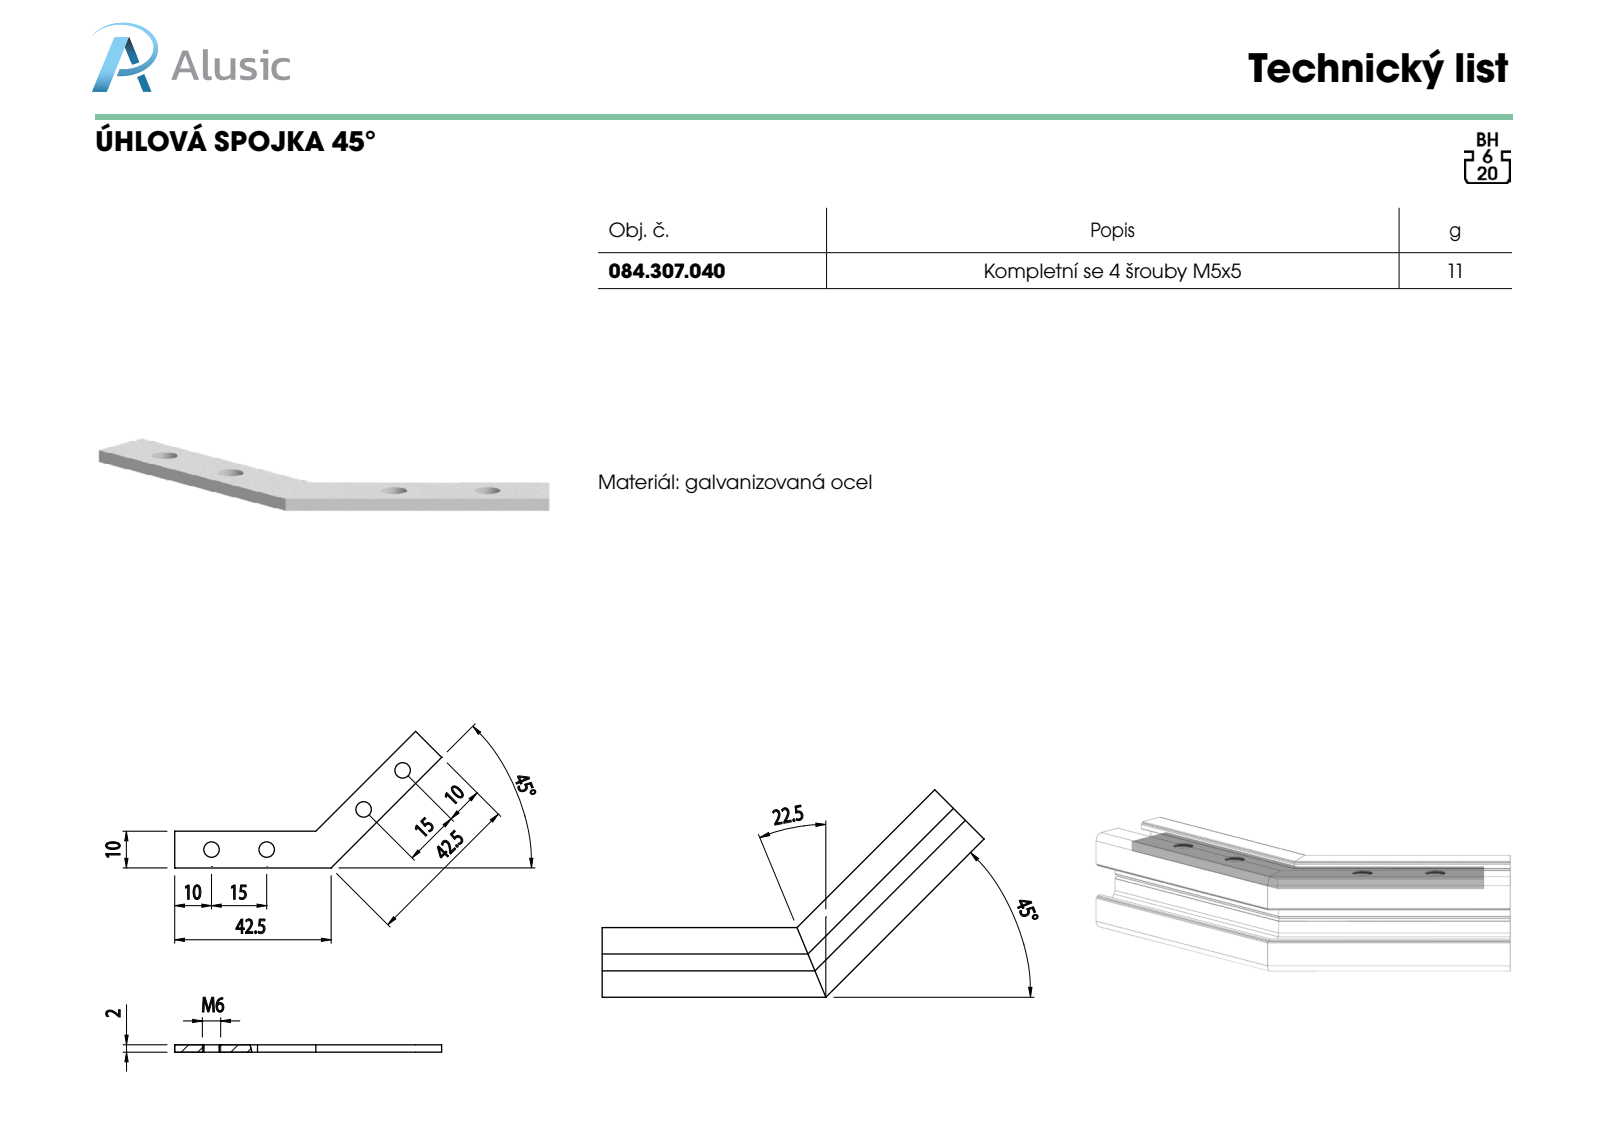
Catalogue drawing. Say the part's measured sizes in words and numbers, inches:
The part is named "084.307.040". Its 3-D file was written by "SolidWorks 2012 (CONFIG_CONTROL_DESIGN)". It is 1 solid with 16 faces: 8 planar, 8 cylindrical and 0 other. Overall it measures 2.856 by 1.461 by 0.079 inches. Its volume is 0.092 cubic inches and its surface area 3.061 square inches. Round holes: 4 of diameter 0.165. The main face-to-face distances are 0.079, 0.394. The hole center spacings are 0.591, 1.683, 1.122, 2.214.
